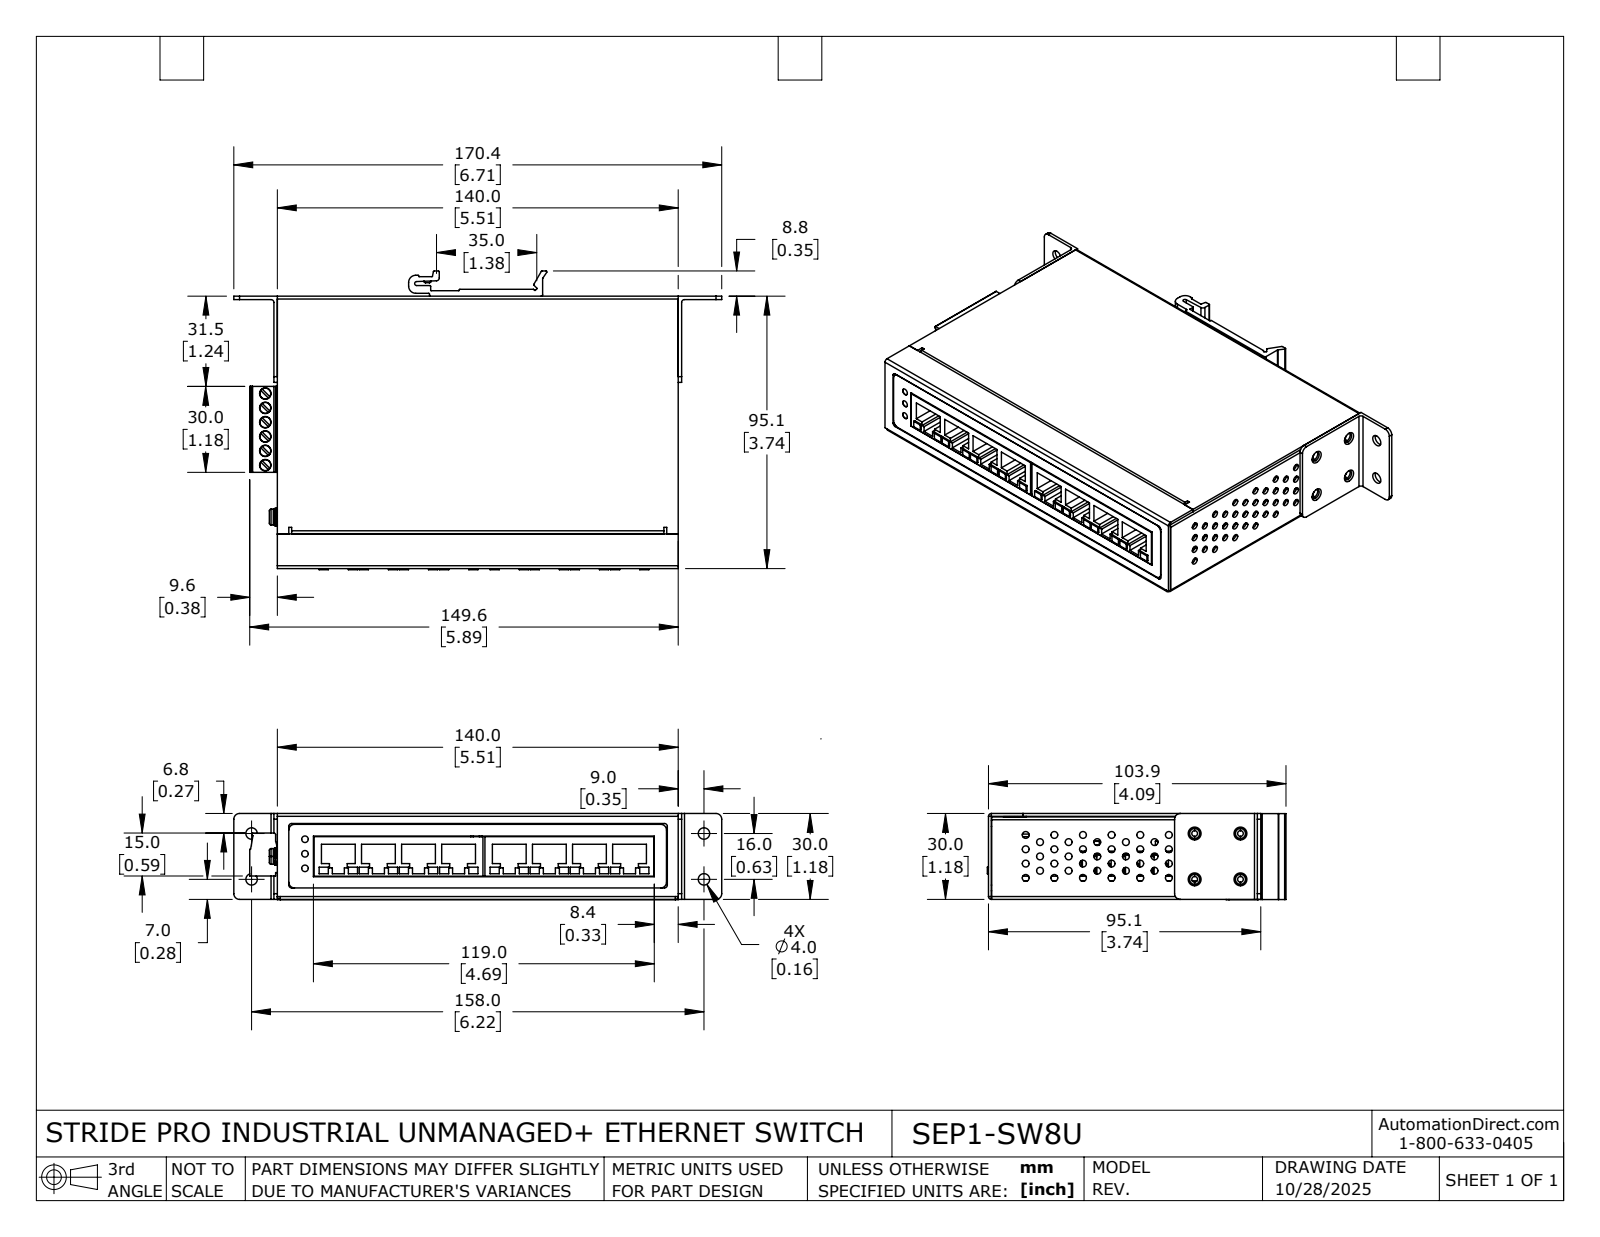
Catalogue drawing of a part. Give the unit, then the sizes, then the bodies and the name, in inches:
Units: inches
Overall size (bounding box): 5.891 × 4.106 × 1.185
Round holes (diameter × count): ⌀0.094 ×51, ⌀0.157 ×13, ⌀0.079 ×9, ⌀0.055 ×6, ⌀0.11 ×5, ⌀0.096 ×4, ⌀0.126 ×4, ⌀0.091 ×3, ⌀0.118 ×3, ⌀0.097 ×2, ⌀0.097 ×2, ⌀0.138 ×2
Round bosses / shafts (diameter × count): ⌀0.118 ×8, ⌀0.157 ×6, ⌀0.149 ×6, ⌀0.035 ×6, ⌀0.197 ×5, ⌀0.165 ×4, ⌀0.157 ×4, ⌀0.149 ×4
Partial cylindrical surfaces — rounded edges, fillets, slot ends (radius × count): R0.004 ×47, R0.01 ×44, R0.039 ×21, R0.079 ×15, R0.012 ×14, R0.008 ×13, R0.115 ×6, R0.12 ×6
Main face-to-face distances: 0.039, 1.142, 0.862, 0.823, 0.063, 0.319, 0.28, 0.886, 0.925, 0.02
Hole centre spacings: 0.394, 0.44, 0.197, 0.22, 0.812, 0.557, 0.599, 0.787
Volume: 5.859 in³ · Surface area: 204.8 in²
Bodies: 20 solids, 2076 faces (1120 planar, 693 cylindrical, 263 other)
Part name (STEP PRODUCT): SEP1-SW8U
STEP written by: SolidWorks 2024 (AUTOMOTIVE_DESIGN)
